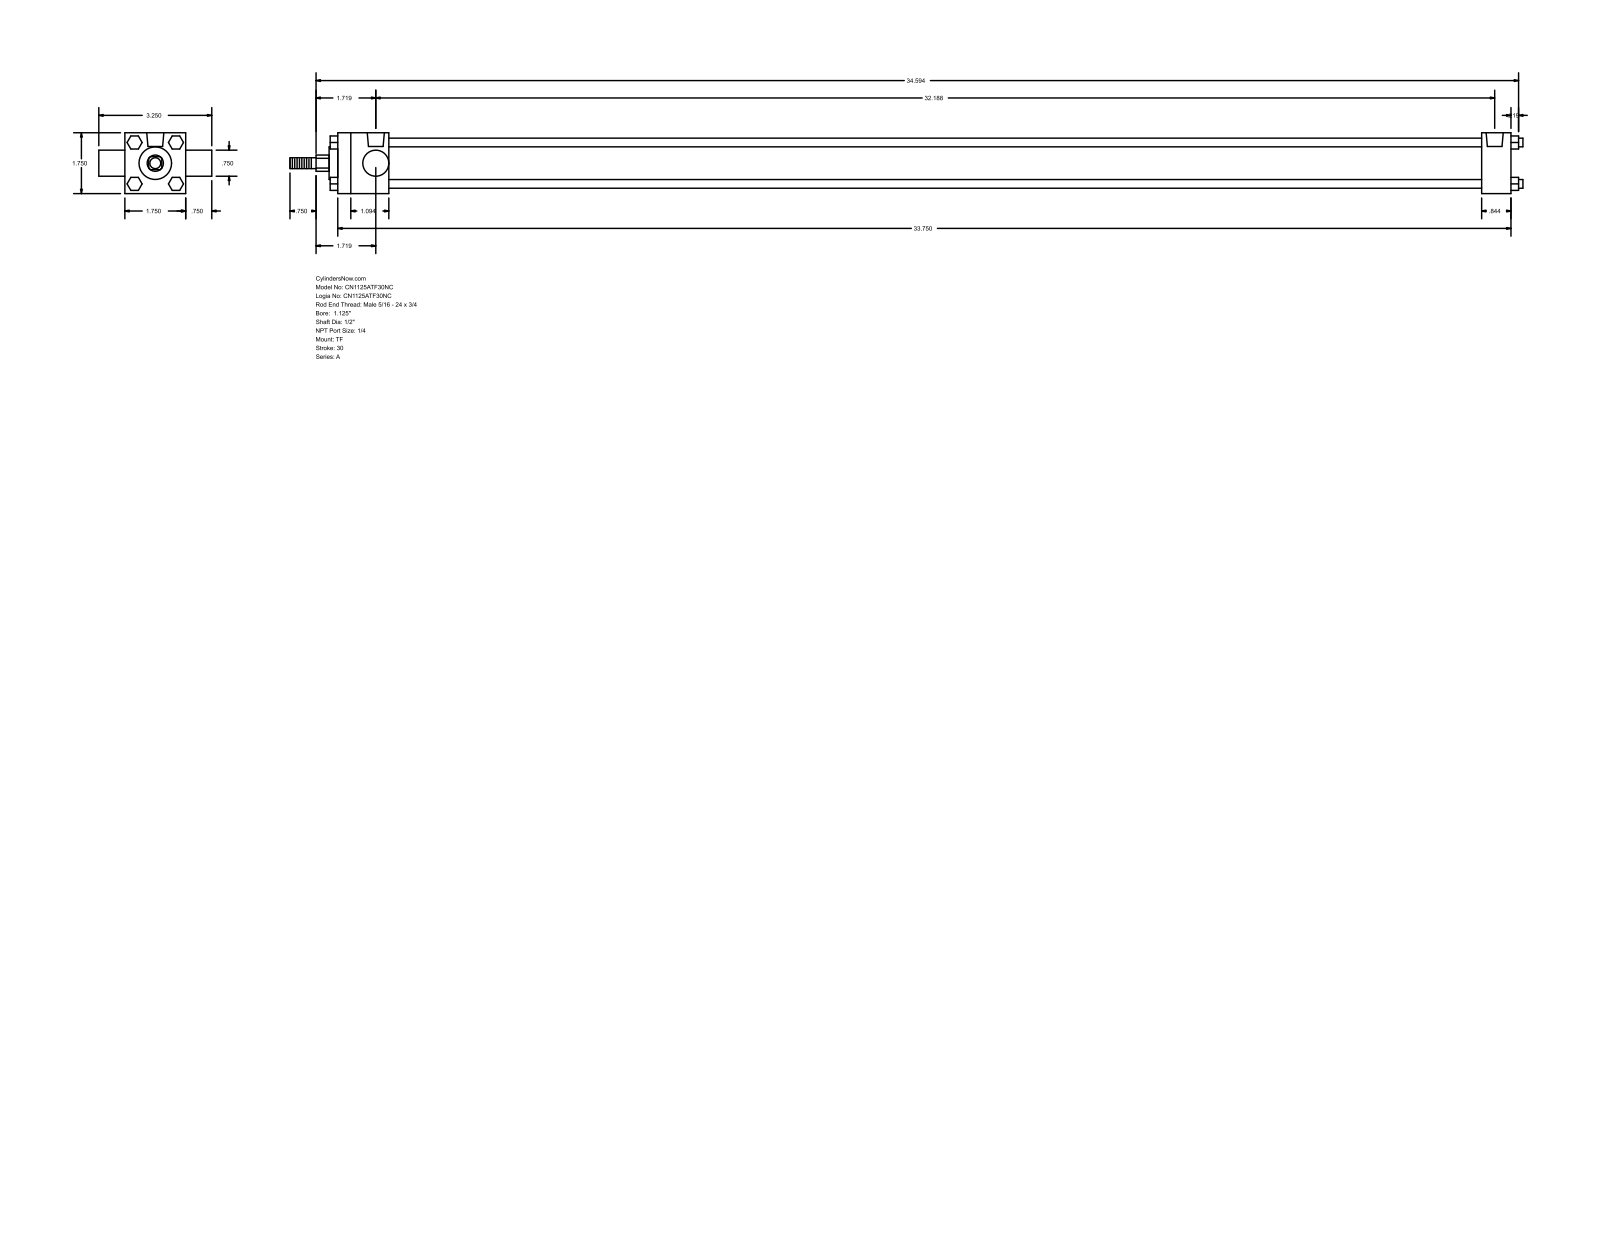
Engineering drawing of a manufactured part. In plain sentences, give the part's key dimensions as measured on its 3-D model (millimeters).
The part is named "A_TF__0112_0.5". Its 3-D file was written by "GSSL Pune (CONFIG_CONTROL_DESIGN)". It is 0 solids with 120 faces: 92 planar, 28 cylindrical and 0 other. Overall it measures 900.91 by 82.55 by 44.45 millimeters. Round holes: 3 of diameter 5.56, 2 of diameter 12.49. Round bosses or shafts: 4 of diameter 6.35, 1 of diameter 31.88, 1 of diameter 23.81, 1 of diameter 19.05, 1 of diameter 12.7, 1 of diameter 7.94. Partial cylindrical surfaces (rounded edges, fillets, slot ends): 1 of radius 5.94. The main face-to-face distances are 44.46, 857.24, 835.81, 21.43, 37.3, 798.51, 819.94, 19.04, 63.5, 9.53. The hole center spacings are 1.58, 1.59, 814.39, 815.97, 815.98, 817.56.
